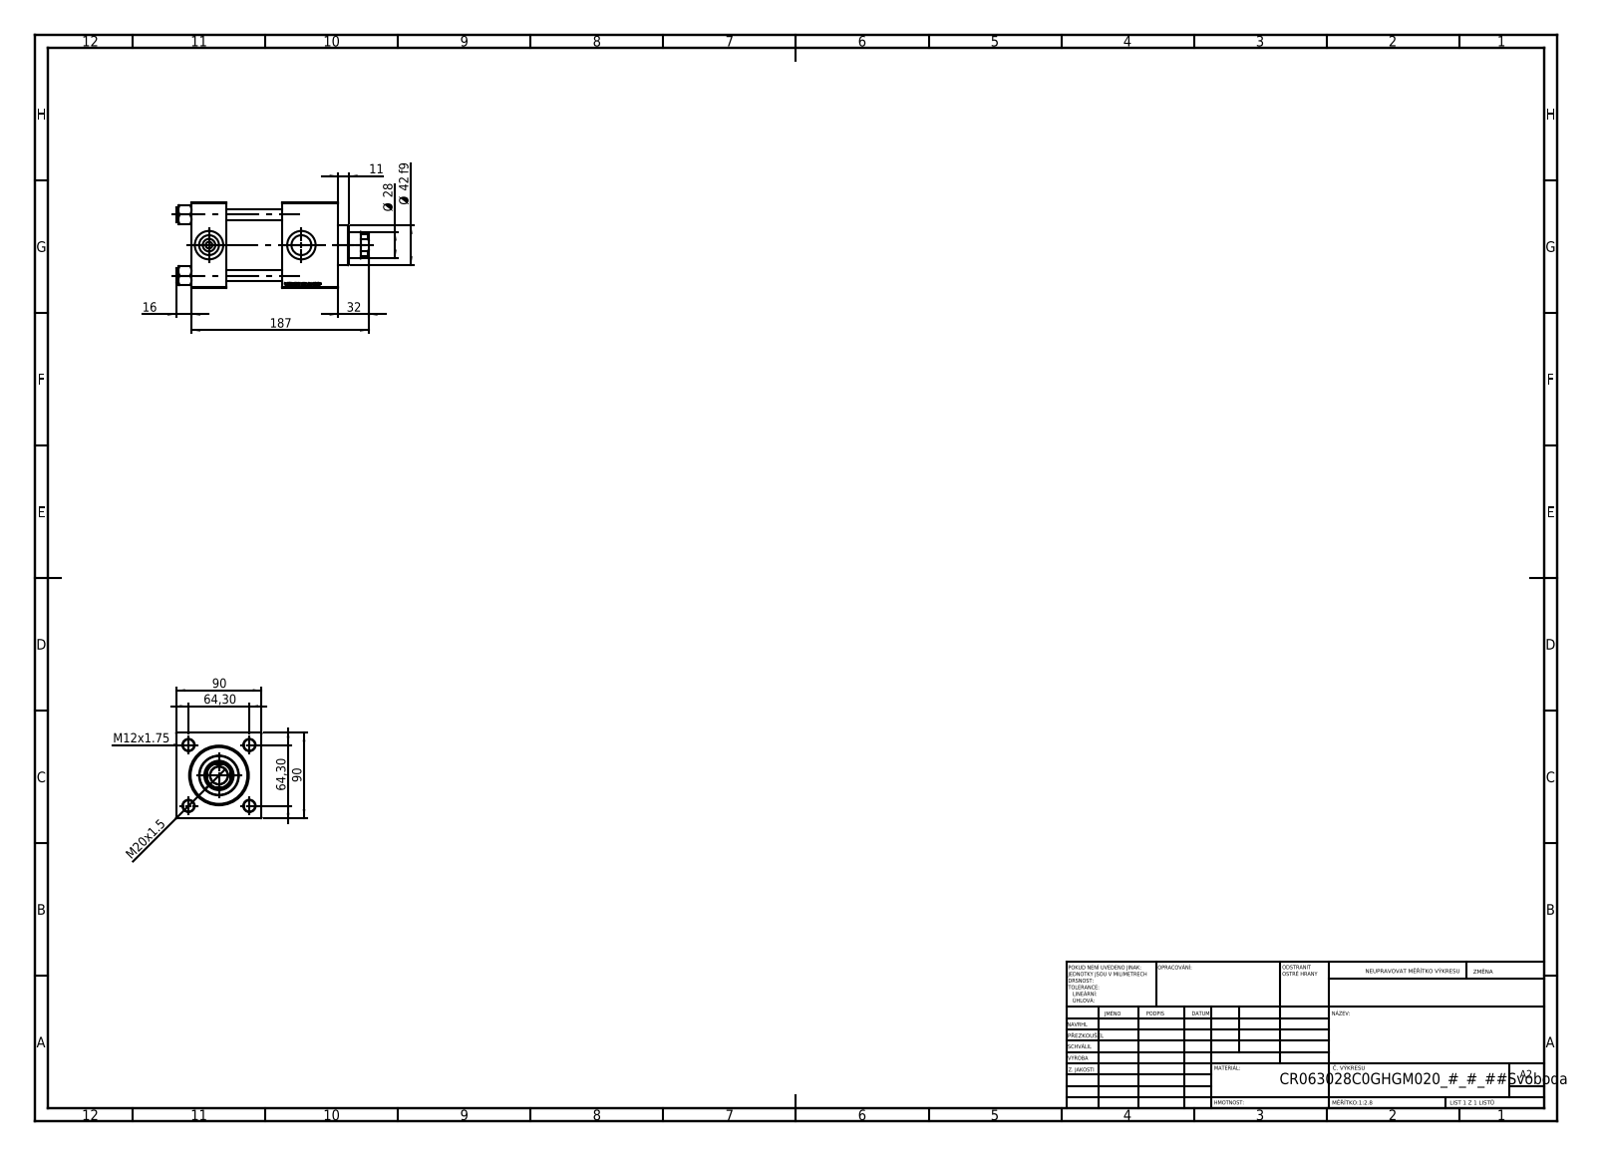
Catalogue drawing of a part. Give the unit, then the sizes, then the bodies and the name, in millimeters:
Units: millimetres
Overall size (bounding box): 203 × 90 × 90
Round holes (diameter × count): ⌀12 ×4, ⌀7 ×2, ⌀20.96 ×2, ⌀30 ×2, ⌀18.5 ×1, ⌀28 ×1, ⌀31 ×1, ⌀50 ×1, ⌀60 ×1, ⌀63 ×1
Round bosses / shafts (diameter × count): ⌀15 ×4, ⌀69 ×1, ⌀42 ×1
Partial cylindrical surfaces — rounded edges, fillets, slot ends (radius × count): R13.5 ×1
Main face-to-face distances: 90, 59, 37, 155, 118, 96, 126.3, 89.3, 30.3, 28.7
Hole centre spacings: 45.47, 64.3, 90.93, 97.5
Volume: 946 885 mm³ · Surface area: 179 128 mm²
Bodies: 11 solids, 1148 faces (526 planar, 86 cylindrical, 536 other)
Part name (STEP PRODUCT): V215CR_C_TYCINKA; V215_VC_A; V215CR_C_Body; V215CR_VCP_C (+1 more)
STEP written by: SolidWorks 2019 (CONFIG_CONTROL_DESIGN)
